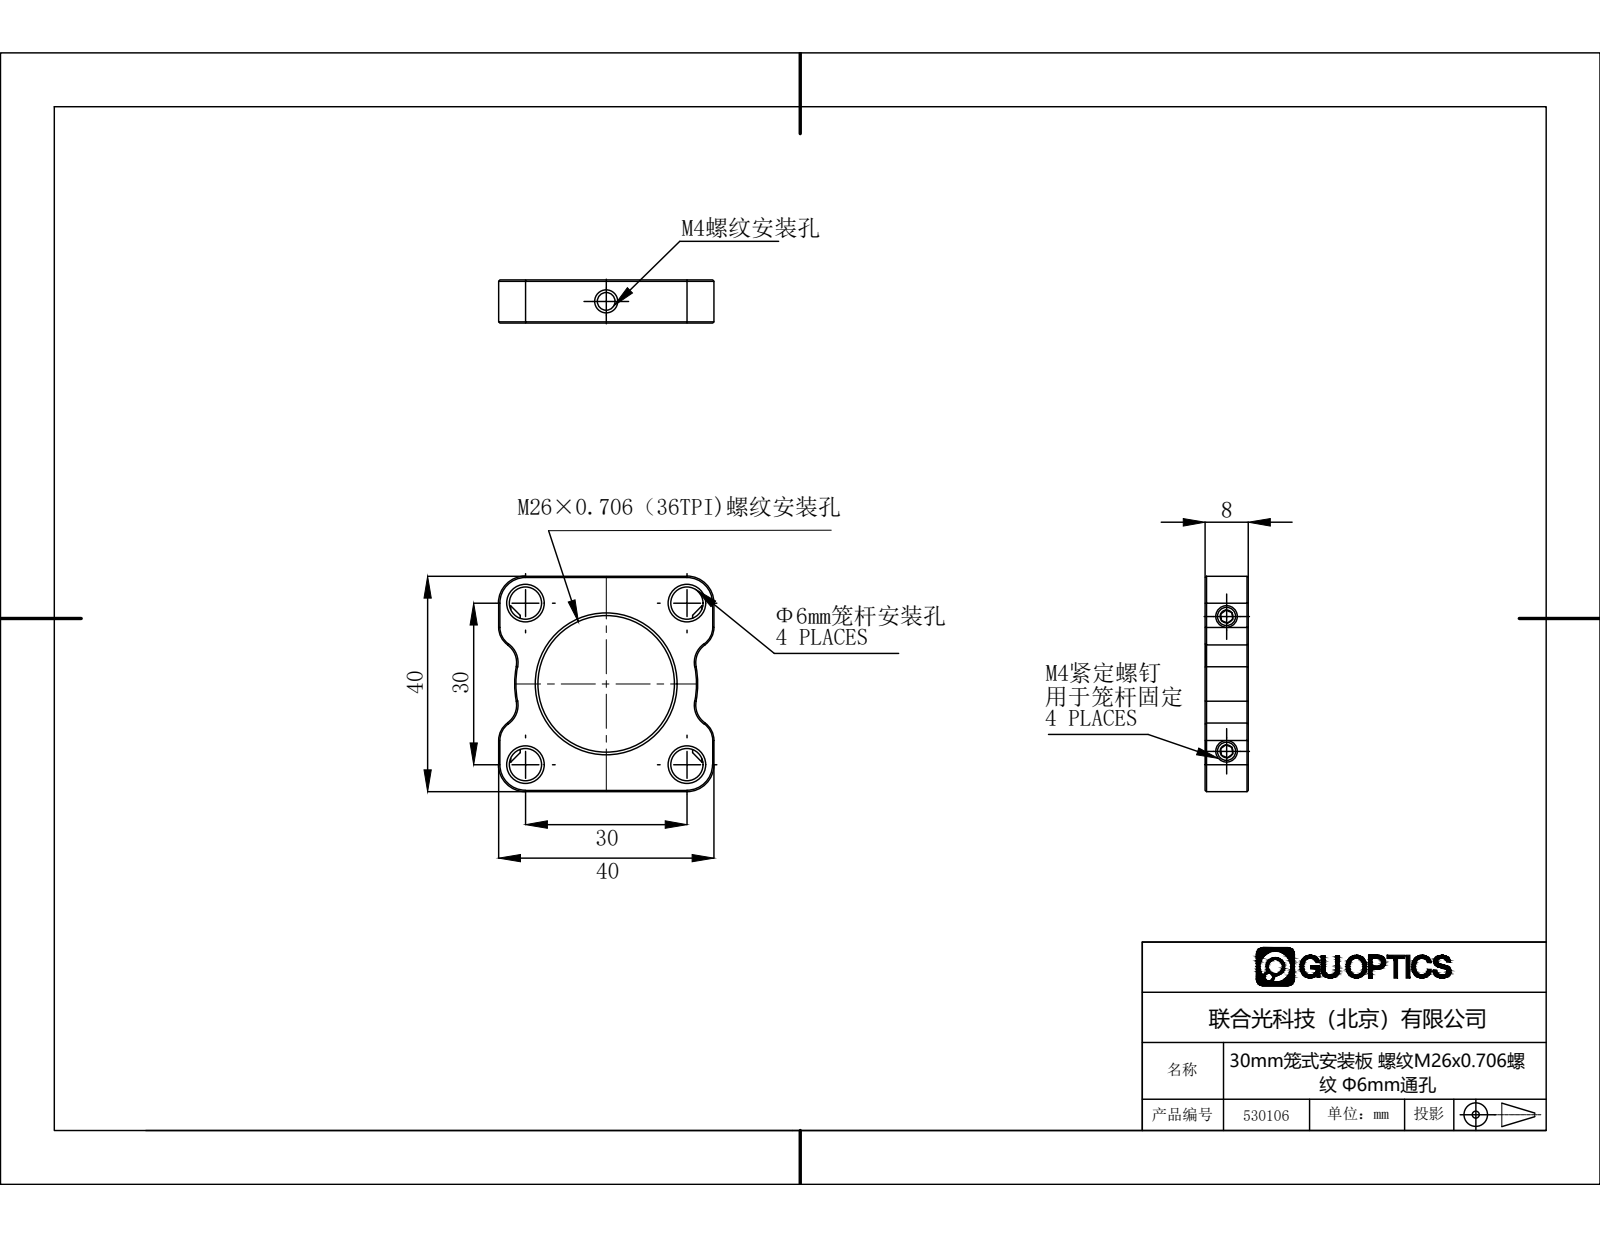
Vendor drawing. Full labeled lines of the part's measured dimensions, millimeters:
Part name (STEP PRODUCT): 530106
STEP written by: SolidWorks 2020 (CONFIG_CONTROL_DESIGN)
Units: millimetres
Bodies: 5 solids, 216 faces (56 planar, 45 cylindrical, 115 other)
Overall size (bounding box): 40 × 40 × 8
Volume: 6 838 mm³ · Surface area: 4 492 mm²
Round holes (diameter × count): ⌀6 ×4, ⌀3.3 ×3, ⌀25.29 ×1
Round bosses / shafts (diameter × count): ⌀4 ×2
Partial cylindrical surfaces — rounded edges, fillets, slot ends (radius × count): R4 ×8, R5 ×4, R17 ×1
Main face-to-face distances: 8, 40, 33.58, 2.1, 2, 38, 23.1, 19.85, 3.25, 36
Hole centre spacings: 21.21, 30, 42.43, 25
